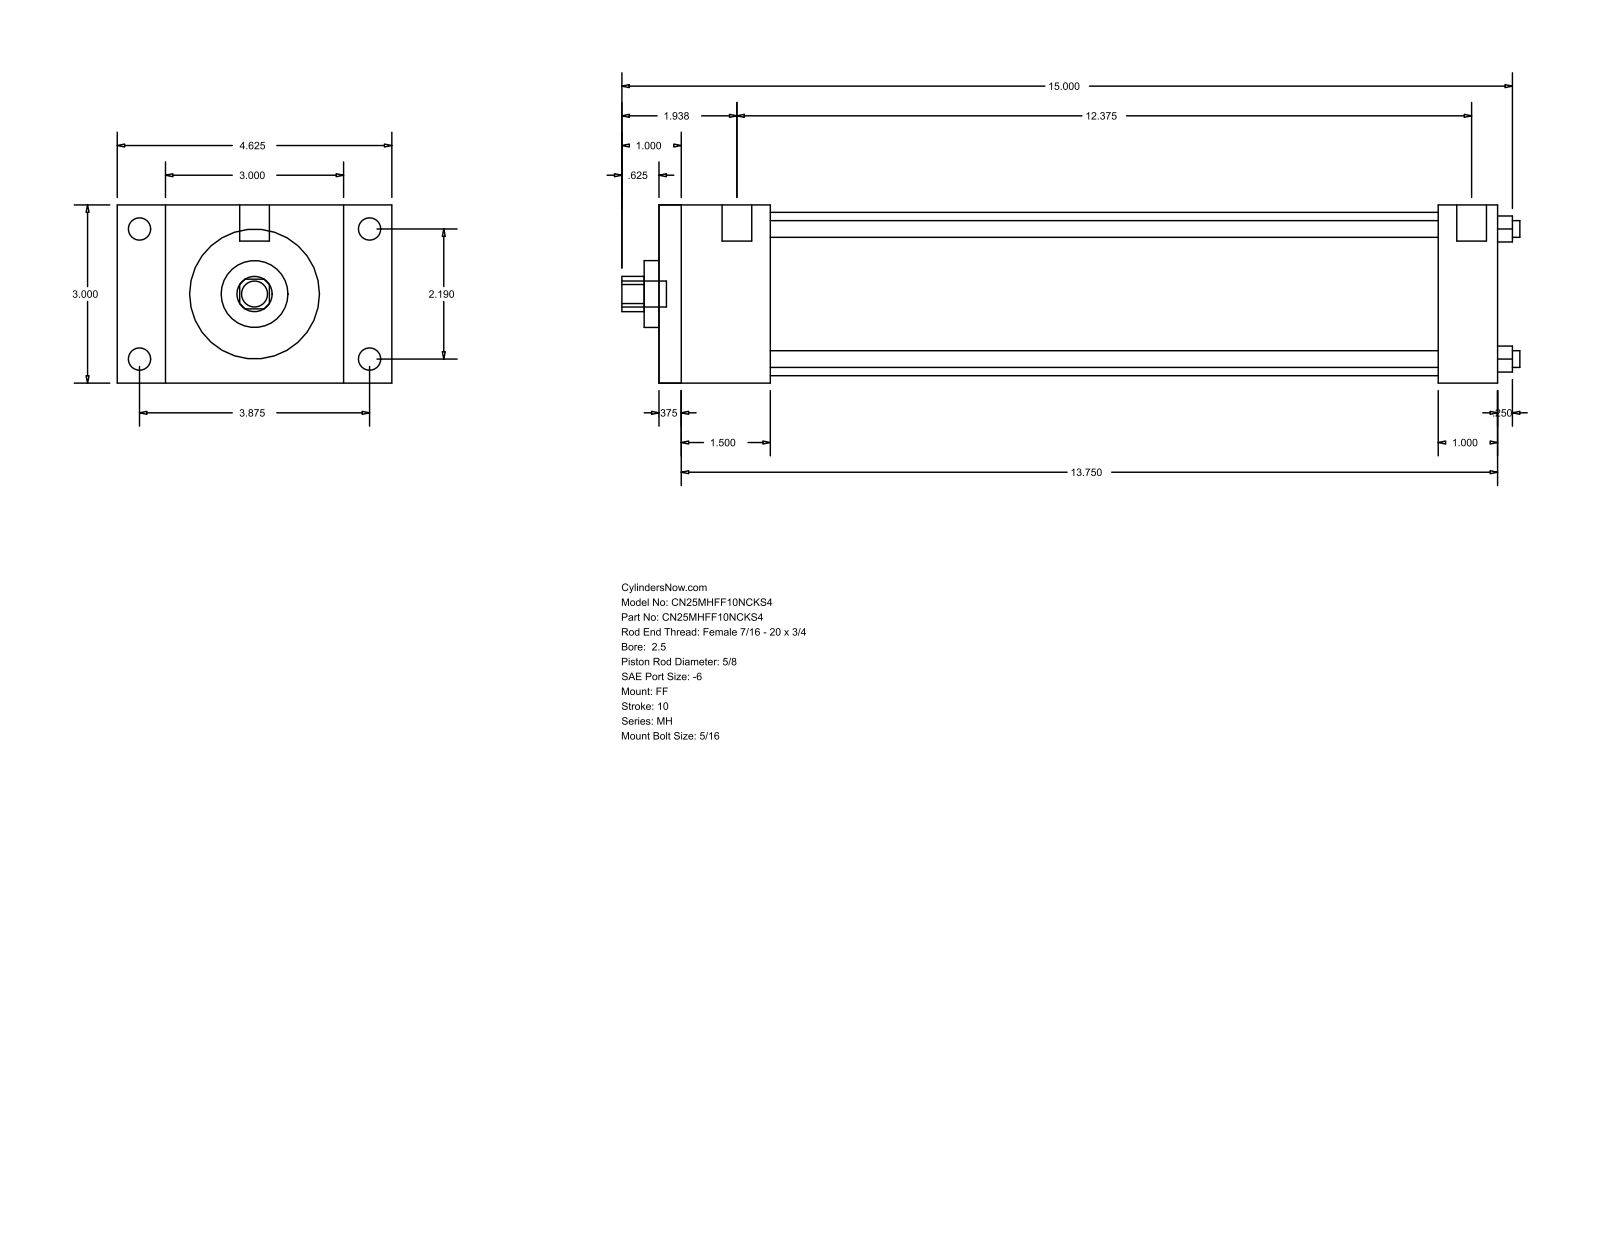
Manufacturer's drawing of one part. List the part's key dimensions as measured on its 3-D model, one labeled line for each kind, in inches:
Part name (STEP PRODUCT): MH_FF__0250_0.625
STEP written by: GSSL Pune (CONFIG_CONTROL_DESIGN)
Units: inches
Bodies: 0 solids, 92 faces (64 planar, 28 cylindrical, 0 other)
Overall size (bounding box): 15.125 × 4.625 × 3
Round holes (diameter × count): ⌀0.281 ×4, ⌀0.625 ×1, ⌀1.125 ×1, ⌀2.75 ×1
Round bosses / shafts (diameter × count): ⌀0.375 ×4, ⌀0.219 ×4, ⌀0.5 ×2, ⌀0.437 ×1
Partial cylindrical surfaces — rounded edges, fillets, slot ends (radius × count): R0.297 ×1
Main face-to-face distances: 3, 14.125, 0.375, 13.75, 1, 1.875, 13.125, 1.5, 12.75, 11.25
Hole centre spacings: 1.548, 2.19, 3.097
